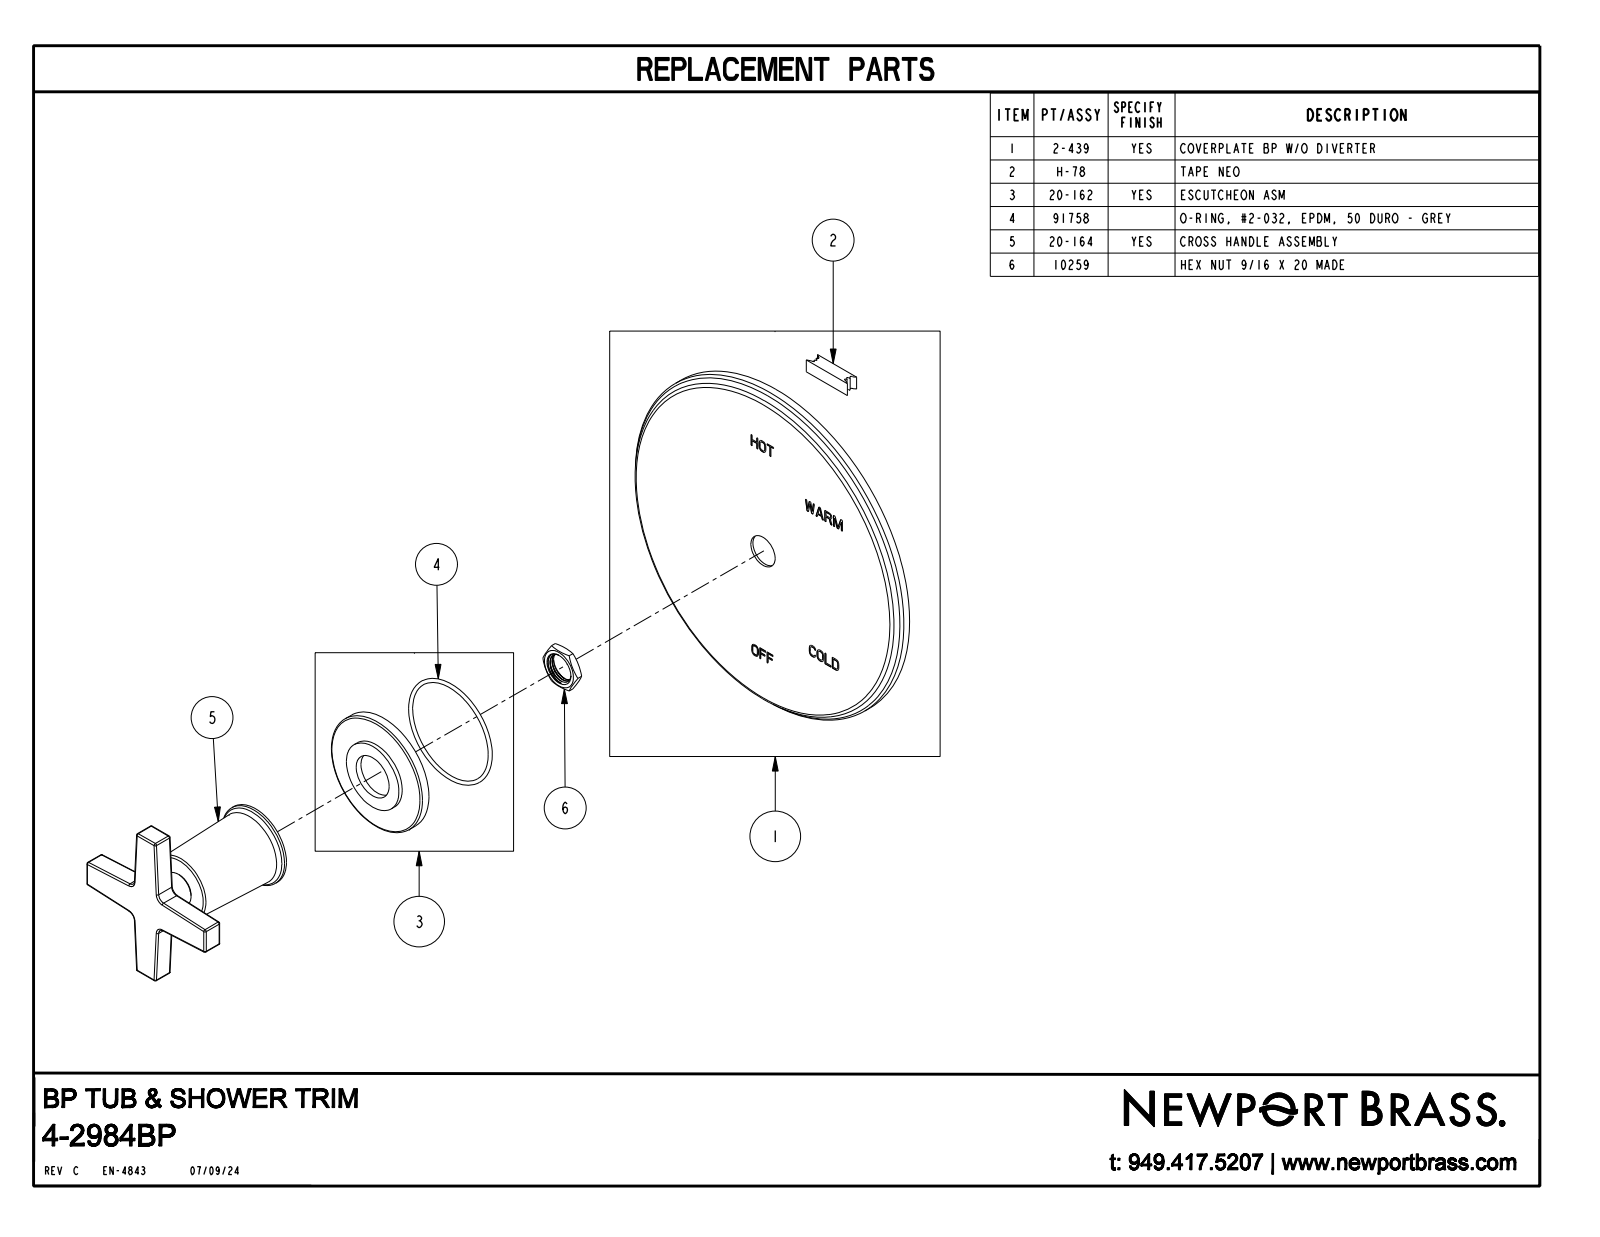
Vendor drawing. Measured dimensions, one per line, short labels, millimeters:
name: 4-2984BP
written by: CREO PARAMETRIC BY PTC INC, 2018400 (CONFIG_CONTROL_DESIGN)
unit: mm
bodies: 1 solid, 437 faces (347 planar, 48 cylindrical, 42 other)
size: 165.1 × 165.1 × 80.8
volume: 237 300 mm³; area: 58 130 mm²
bosses: 1× ⌀165.1, 1× ⌀55.9, 1× ⌀38.1, 1× ⌀32.4, 1× ⌀15.9, 1× ⌀13.3
rounds: 32× R0.8, 4× R3.2
face distances: 8, 80.8, 72.9, 4.7, 12.7, 68.1, 71.3, 63.4, 58.6, 9.5
